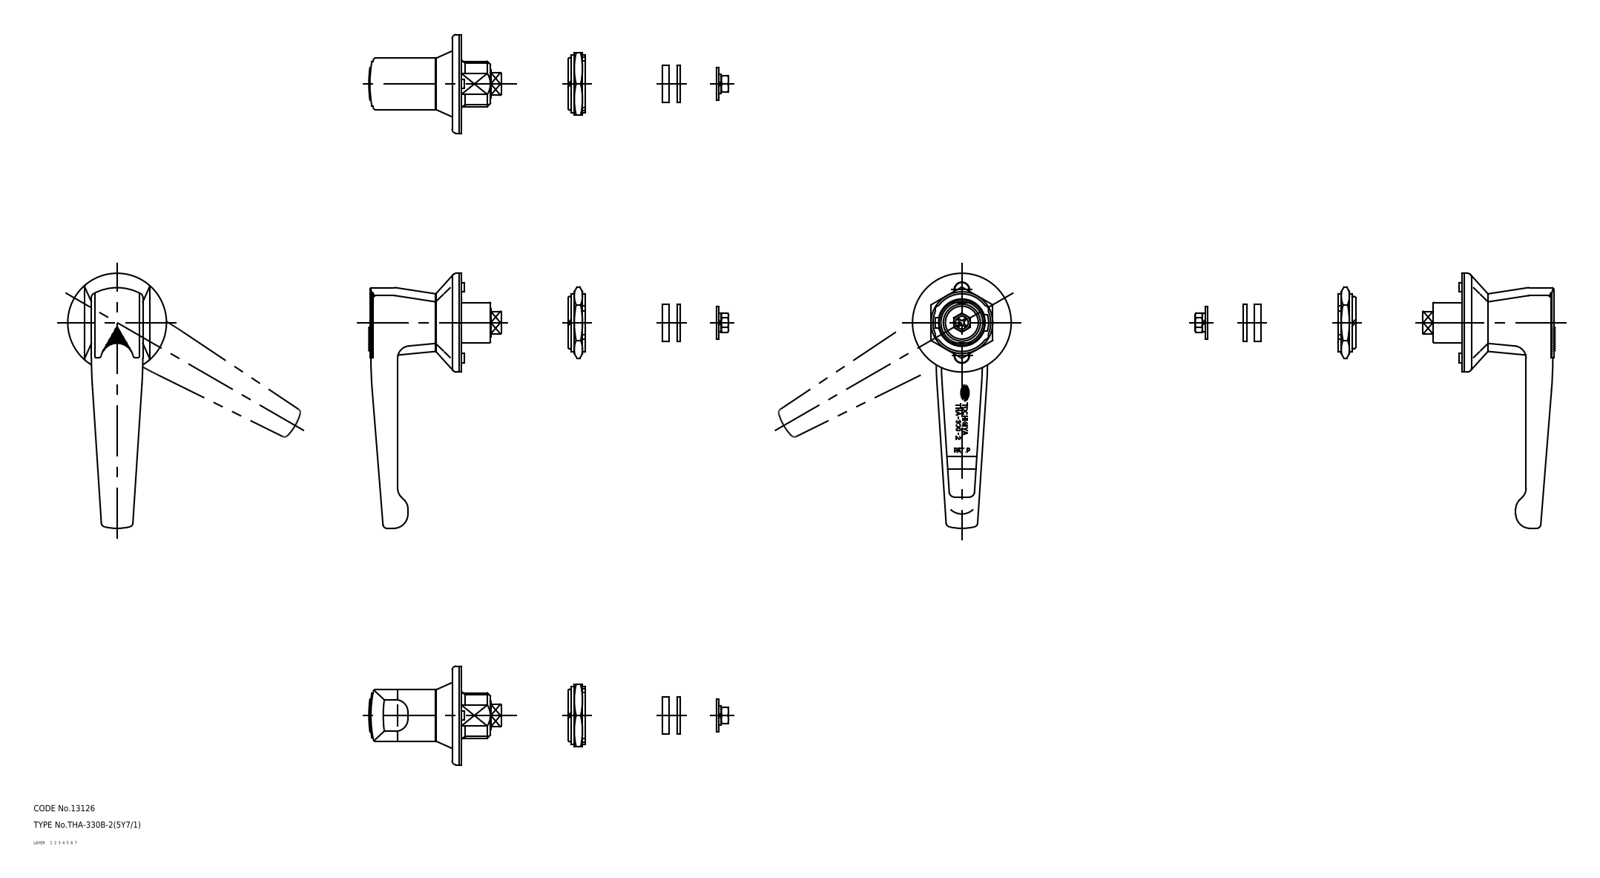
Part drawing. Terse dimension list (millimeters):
name: washer_D; washer_C; washer_B; washer_A (+6 more)
written by: CADfix (AUTOMOTIVE_DESIGN)
unit: mm
bodies: 9 solids, 332 faces (0 planar, 0 cylindrical, 332 other)
size: 124 × 70.3 × 48
volume: 58 356 mm³; area: 26 166 mm²
